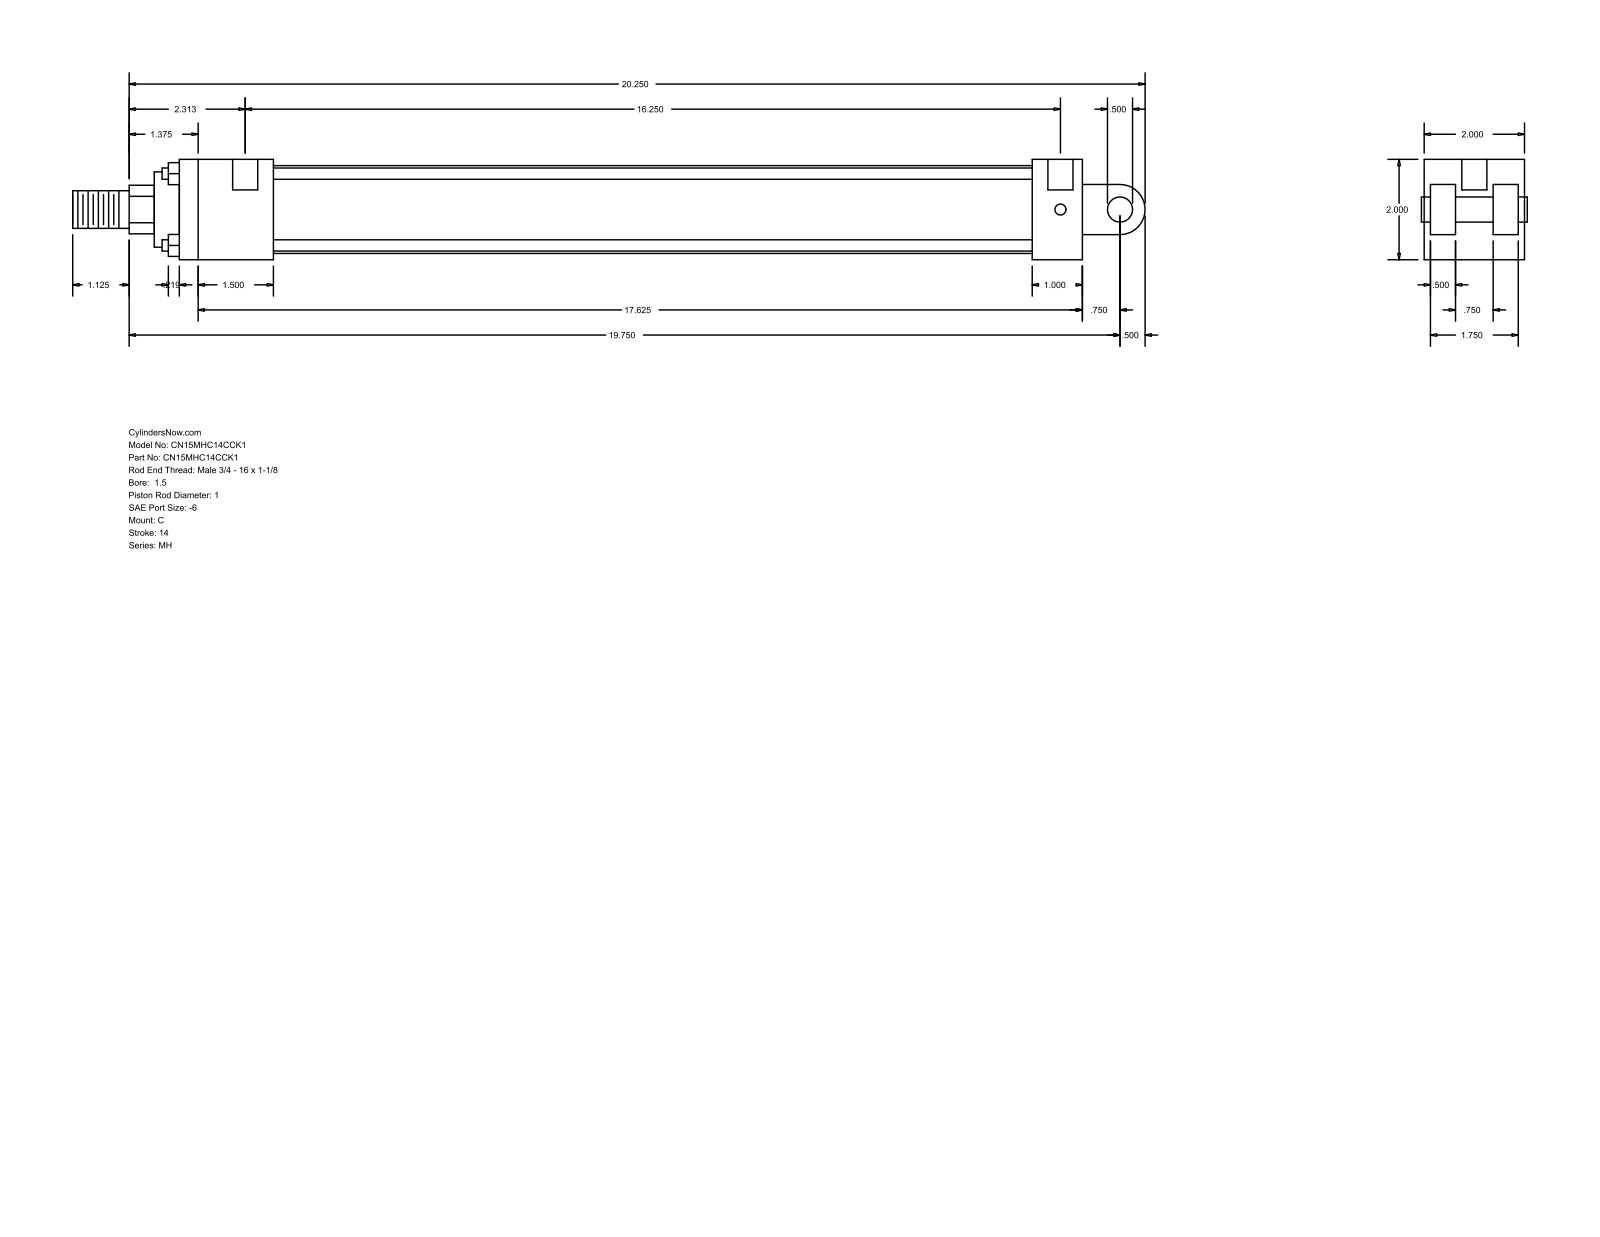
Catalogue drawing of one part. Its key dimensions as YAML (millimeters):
part_name: "MH_C__0150_1"
step_written_by: "GSSL Pune (CONFIG_CONTROL_DESIGN)"
units: millimeters
bodies: {solids: 0, faces: 99, planar: 70, cylindrical: 29, other: 0}
overall_size: [542.92, 50.8, 50.8]
round_holes:
  - {diameter: 5.56, count: 4}
  - {diameter: 12.7, count: 2}
round_bosses_or_shafts:
  - {diameter: 5.71, count: 4}
  - {diameter: 44.45, count: 1}
  - {diameter: 38.1, count: 1}
  - {diameter: 25.4, count: 1}
  - {diameter: 19.05, count: 1}
  - {diameter: 12.7, count: 1}
partial_cylinders:
  - {radius: 12.29, count: 1}
  - {radius: 12.7, count: 1}
face_to_face_distances: [50.8, 12.7, 47.63, 25.4, 3.17, 15.87, 34.93, 31.76, 457.2, 38.1]
hole_center_spacings: [415.93, 3.18, 412.75]
